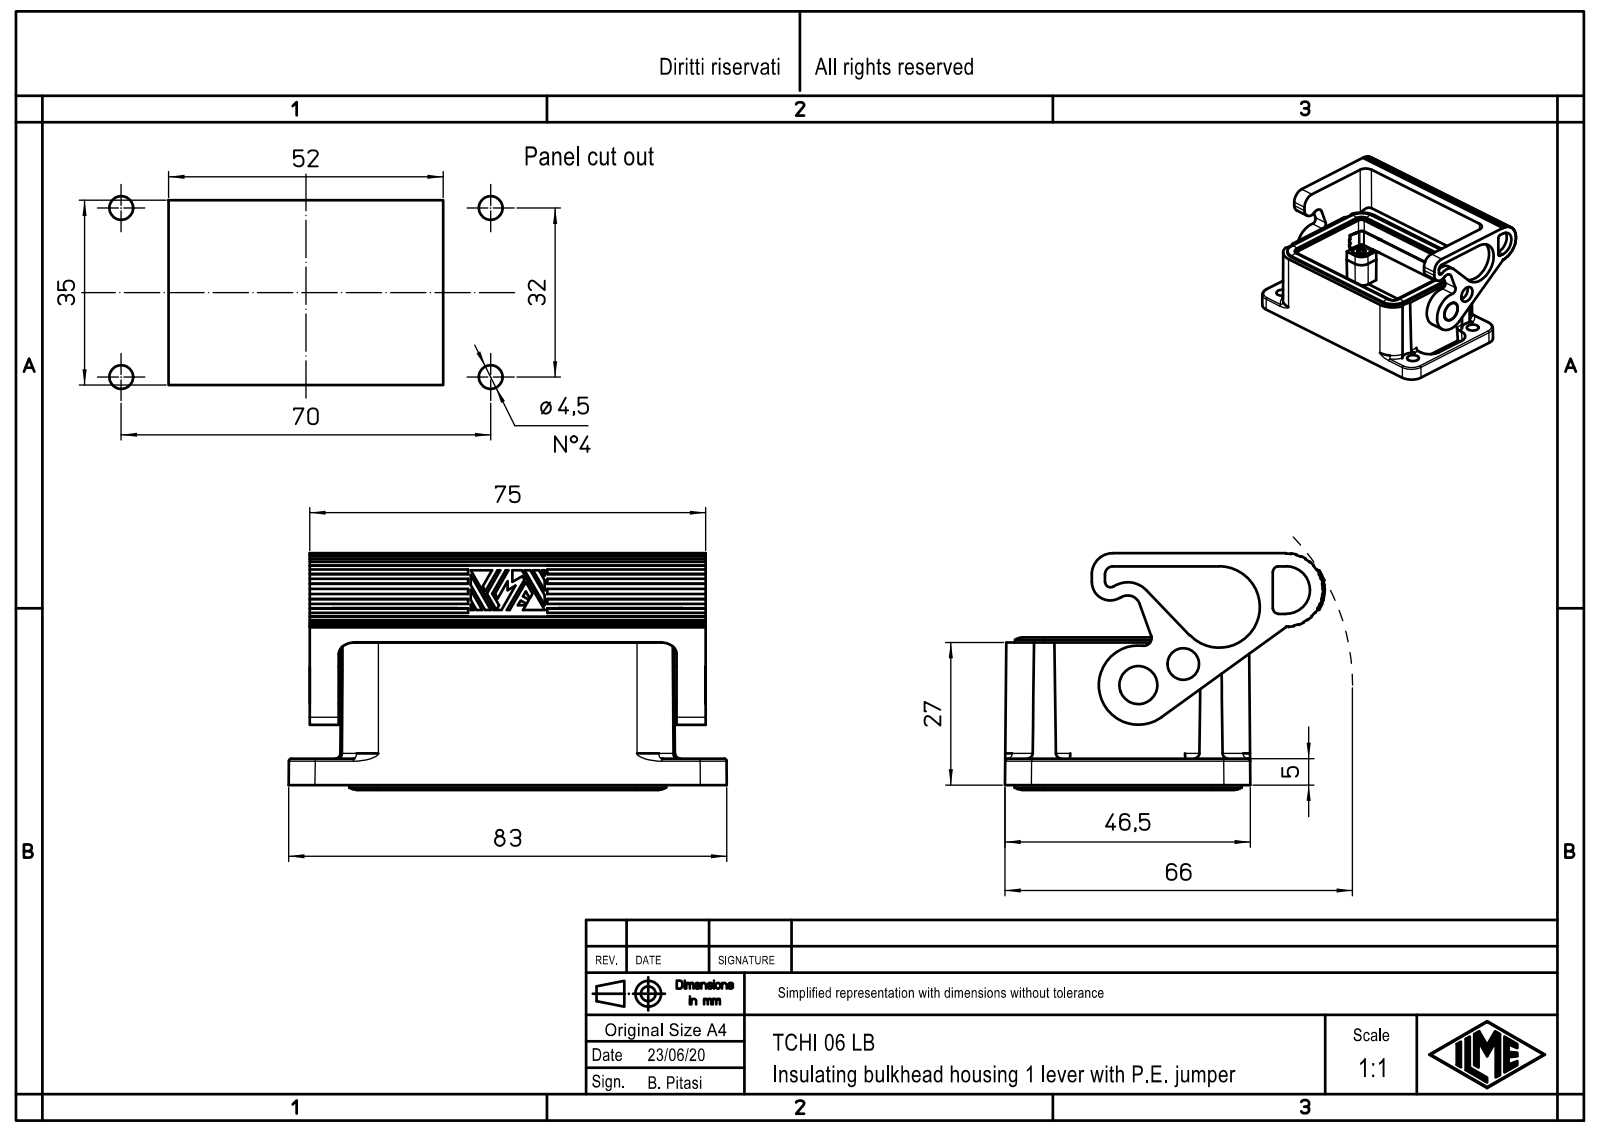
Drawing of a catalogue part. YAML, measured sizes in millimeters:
part_name: "TCHI_06_LB"
step_written_by: "Creo Elements/Direct Modeling 20.1B 02-Apr-2019 (C) Parametric Technology GmbH (AUTOMOTIVE_DESIGN)"
units: millimeters
bodies: {solids: 1, faces: 593, planar: 290, cylindrical: 195, other: 108}
overall_size: [83, 60.54, 44.84]
volume: 52030
surface_area: 27037
round_holes:
  - {diameter: 3, count: 4}
  - {diameter: 3.5, count: 4}
  - {diameter: 4.5, count: 4}
  - {diameter: 6, count: 1}
  - {diameter: 10, count: 1}
round_bosses_or_shafts:
  - {diameter: 4.8, count: 4}
  - {diameter: 4.75, count: 4}
  - {diameter: 7, count: 1}
partial_cylinders:
  - {radius: 1.5, count: 18}
  - {radius: 2.44, count: 8}
  - {radius: 2.7, count: 8}
  - {radius: 5, count: 8}
  - {radius: 5.5, count: 8}
  - {radius: 3.5, count: 5}
  - {radius: 0.5, count: 4}
  - {radius: 1, count: 4}
face_to_face_distances: [40.6, 57.61, 5.5, 69.5, 2.5, 3, 72.5, 67, 34.1, 64]
hole_center_spacings: [13.24, 32.24, 57.05, 64.18, 27, 32, 44, 51.62]
